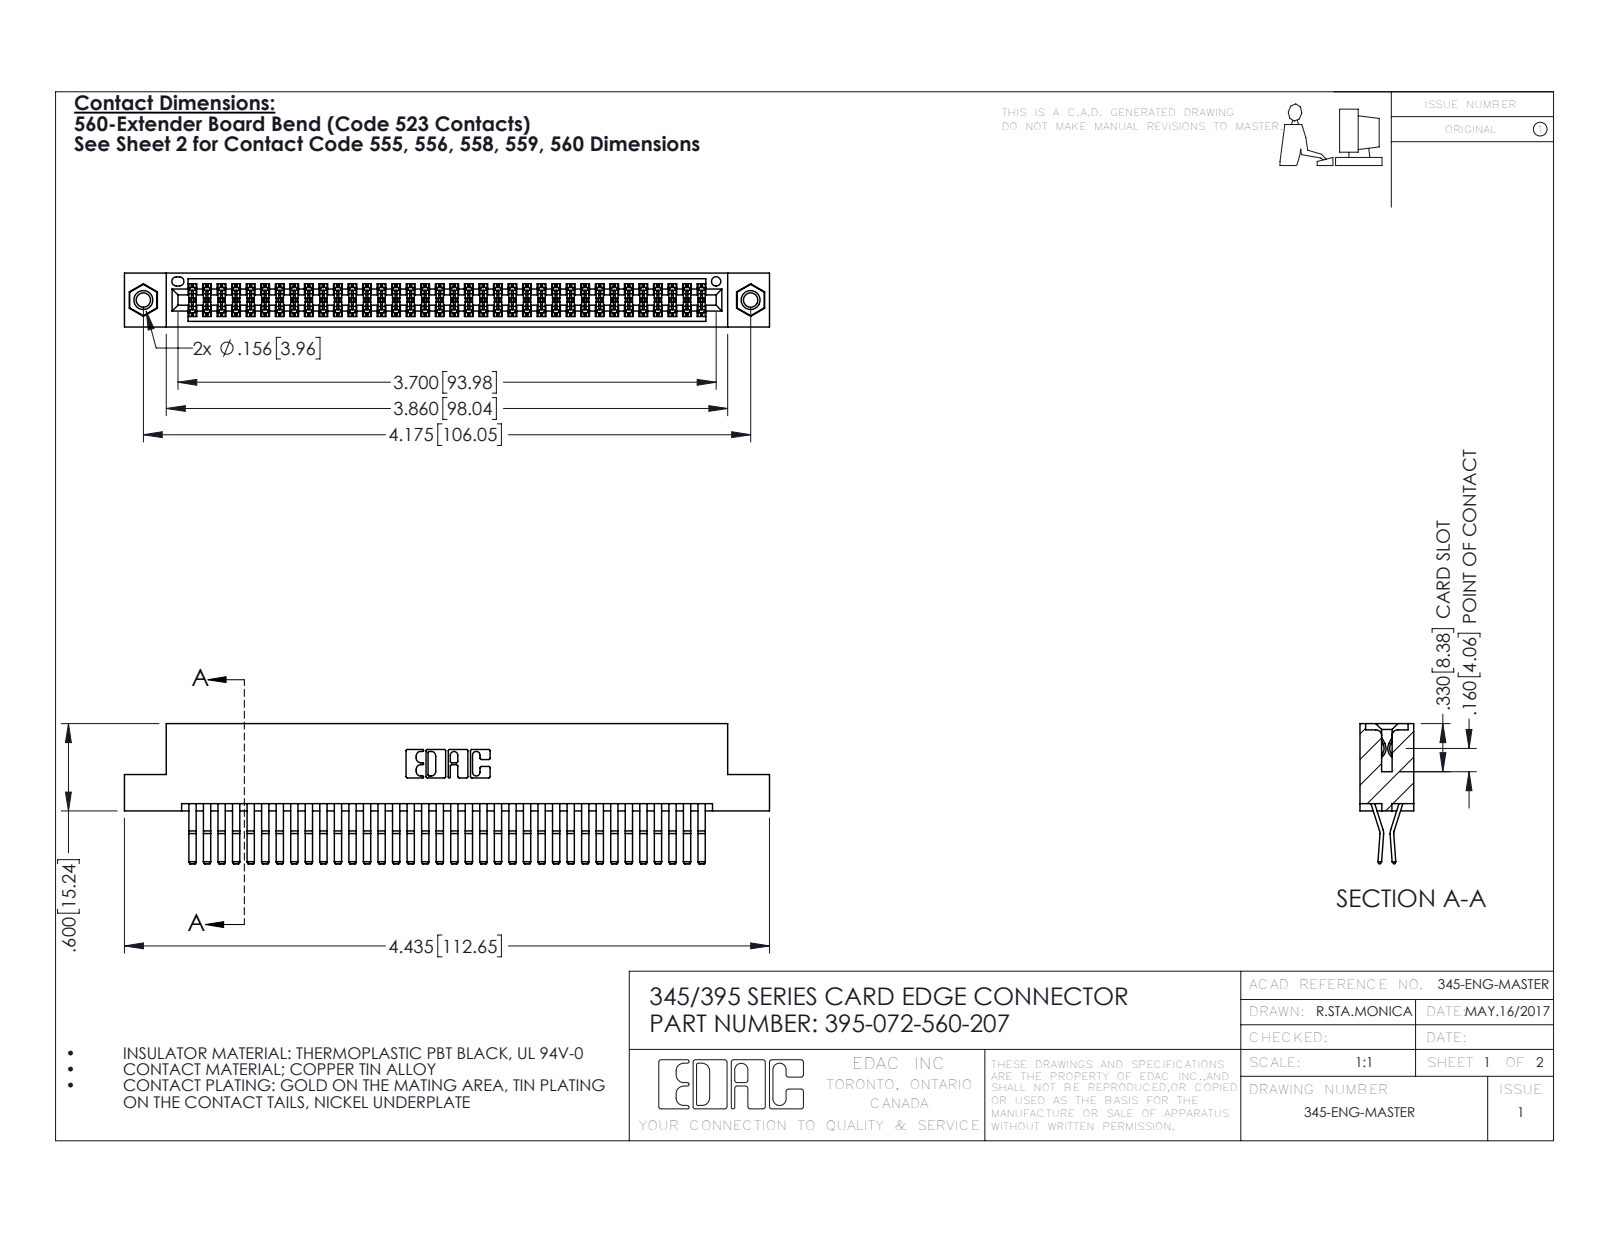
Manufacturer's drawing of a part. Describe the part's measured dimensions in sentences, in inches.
The part is named "345 Part_Flush Mounting Lugs - 0.156 Dia-TI; 345-292-001_560 Tail; 395-072-560-207; 345-250-001_345-250-005-103". Its 3-D file was written by "SolidWorks 2016 (CONFIG_CONTROL_DESIGN)". It is 75 solids with 3930 faces: 2488 planar, 1426 cylindrical and 16 other. Overall it measures 4.435 by 0.962 by 0.37 inches. Its volume is 0.692 cubic inches and its surface area 27.74 square inches. Round holes: 2 of diameter 0.098, 2 of diameter 0.125, 2 of diameter 0.156, 1 of diameter 0.064. Round bosses or shafts: 2 of diameter 0.155. Partial cylindrical surfaces (rounded edges, fillets, slot ends): 108 of radius 0.006, 22 of radius 0.01, 6 of radius 0.007, 6 of radius 0.031, 3 of radius 0.026, 2 of radius 0.01, 2 of radius 0.014, 2 of radius 0.019. The main face-to-face distances are 0.025, 0.072, 0.298, 0.37, 0.2, 0.098, 0.272, 0.225, 0.175, 0.149. The hole center spacings are 0.27, 3.939, 4.175.
